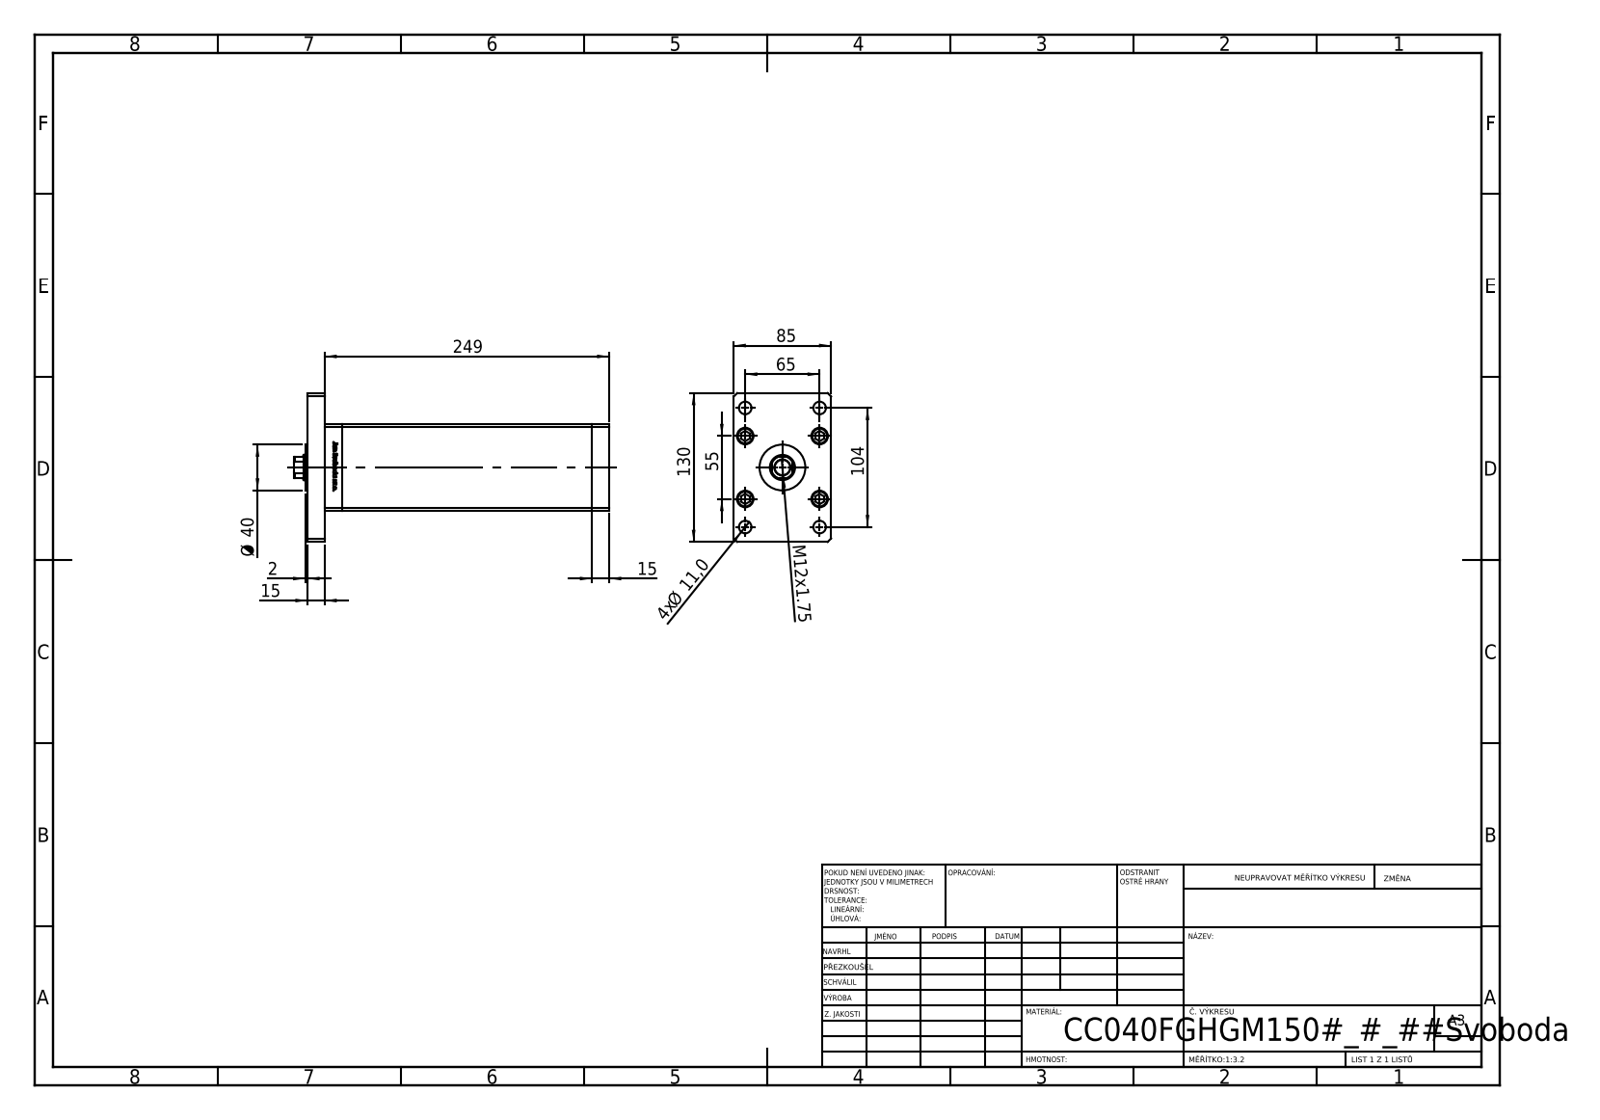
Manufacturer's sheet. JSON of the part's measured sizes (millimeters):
{"part_name": "ALLEN BOLT; V220C_VC_F; V220C_FRONT_F; V220C_F (+2 more)", "step_written_by": "SolidWorks 2019 (CONFIG_CONTROL_DESIGN)", "units": "millimeters", "bodies": {"solids": 19, "faces": 1308, "planar": 515, "cylindrical": 187, "other": 606}, "overall_size": [275, 130, 85], "volume_mm3": 1536000, "surface_area_mm2": 236256, "round_holes": [[11, 9], [15.5, 5], [10, 4], [14.5, 4], [2, 2], [13.16, 2], [13.5, 1], [22, 1], [23.5, 1]], "round_bosses_or_shafts": [[8, 9], [14.5, 5], [40, 1]], "partial_cylinders_radius": [[0.93, 2], [10.5, 1]], "face_to_face_distances": [15, 85, 75, 233.5, 248.5, 218.5, 30, 263.5, 10.5, 27.5], "hole_center_spacings": [28, 24.5, 42.57, 61.32, 65, 69.46, 79.5, 102.69]}
